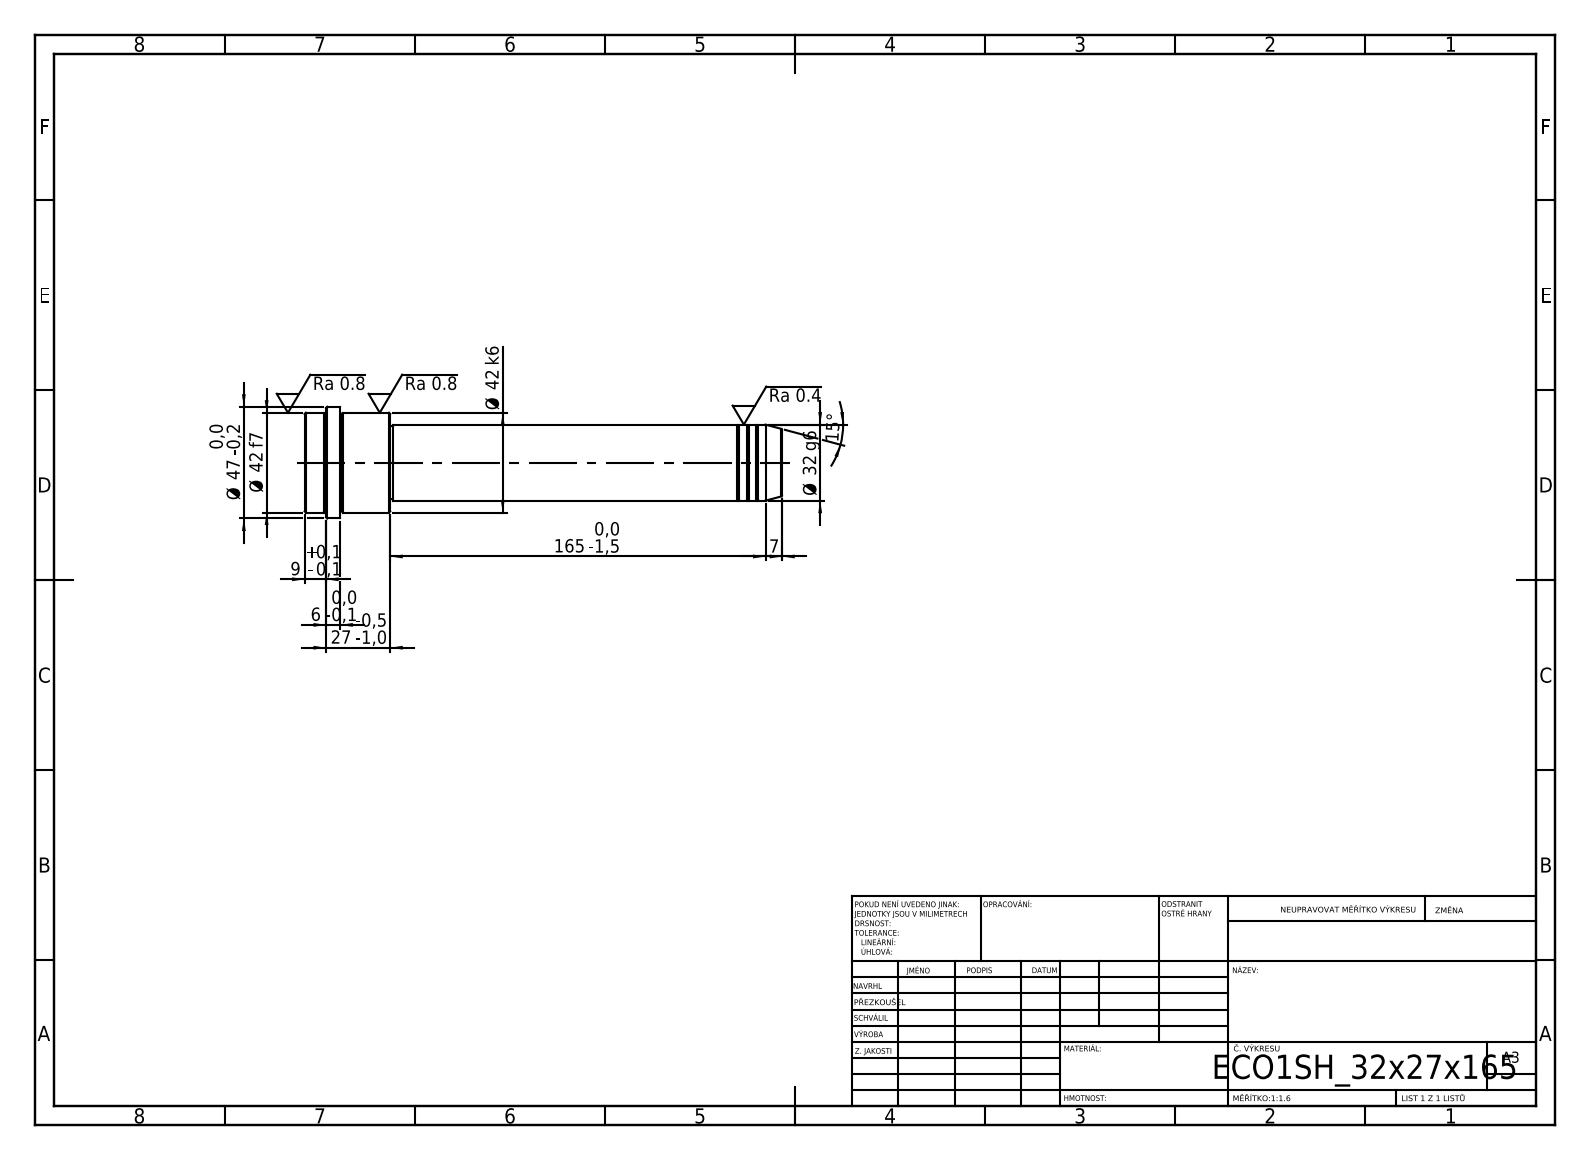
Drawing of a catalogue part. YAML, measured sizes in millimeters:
step_written_by: "SolidWorks 2019 (CONFIG_CONTROL_DESIGN)"
units: millimeters
bodies: {solids: 1, faces: 52, planar: 6, cylindrical: 16, other: 30}
overall_size: [201, 47, 47]
volume: 183717
surface_area: 24978
round_bosses_or_shafts:
  - {diameter: 47, count: 1}
  - {diameter: 42, count: 1}
  - {diameter: 32, count: 1}
  - {diameter: 31, count: 1}
face_to_face_distances: [201, 165, 36, 186, 21, 15, 192, 27, 6, 9]
